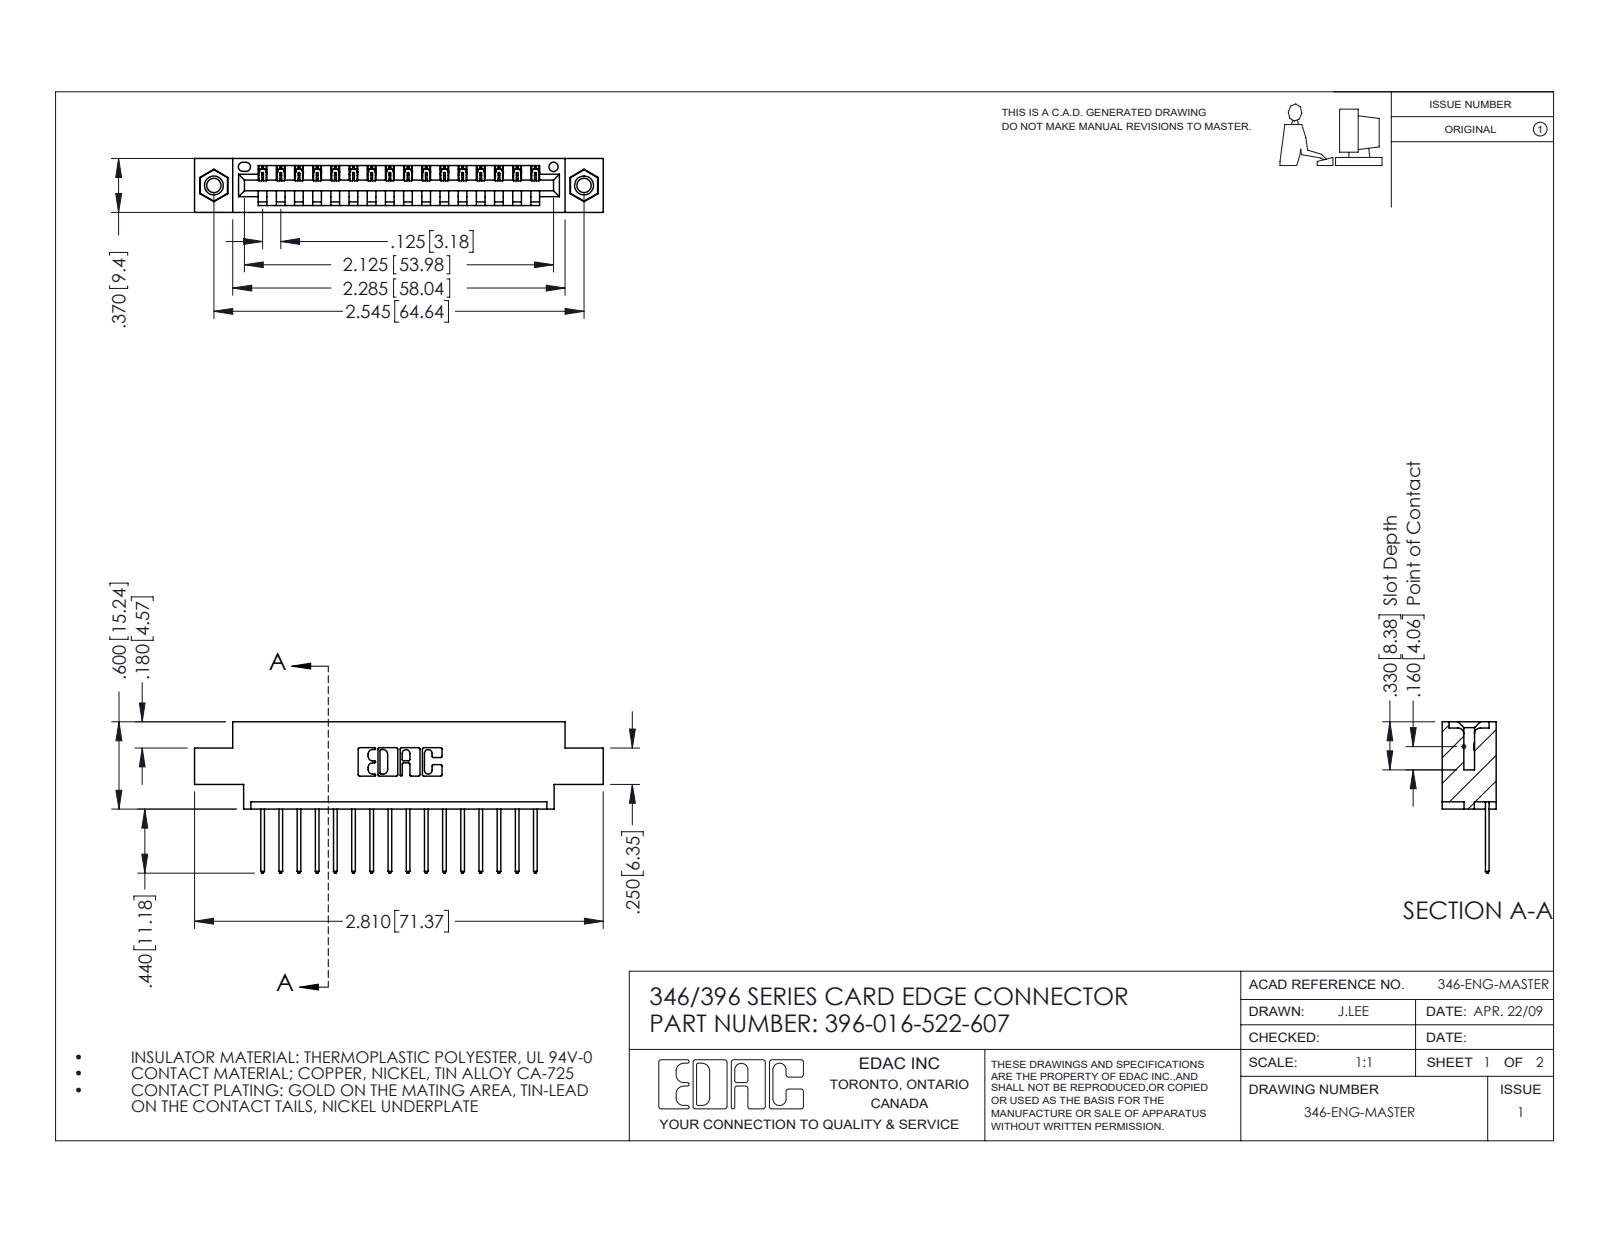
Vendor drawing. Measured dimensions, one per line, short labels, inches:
name: 346 Part_0.170 Offset - 0.156 Dia-TI; 396-016-522-607; 345-250-001_345-250-005-103; 345-292-001_345-293-122
written by: SolidWorks 2016 (CONFIG_CONTROL_DESIGN)
unit: in
bodies: 19 solids, 1114 faces (752 planar, 346 cylindrical, 16 other)
size: 2.81 × 1.04 × 0.37
volume: 0.396 in³; area: 12.53 in²
holes: 2× ⌀0.098, 2× ⌀0.125, 2× ⌀0.156, 1× ⌀0.064
bosses: 2× ⌀0.155
rounds: 32× R0.006, 32× R0.01, 22× R0.01, 6× R0.007, 6× R0.031, 3× R0.026, 2× R0.031, 2× R0.04
face distances: 0.048, 0.322, 0.37, 0.25, 0.072, 0.298, 0.025, 0.222, 0.148, 0.1
hole spacings: 0.246, 2.338, 2.545
